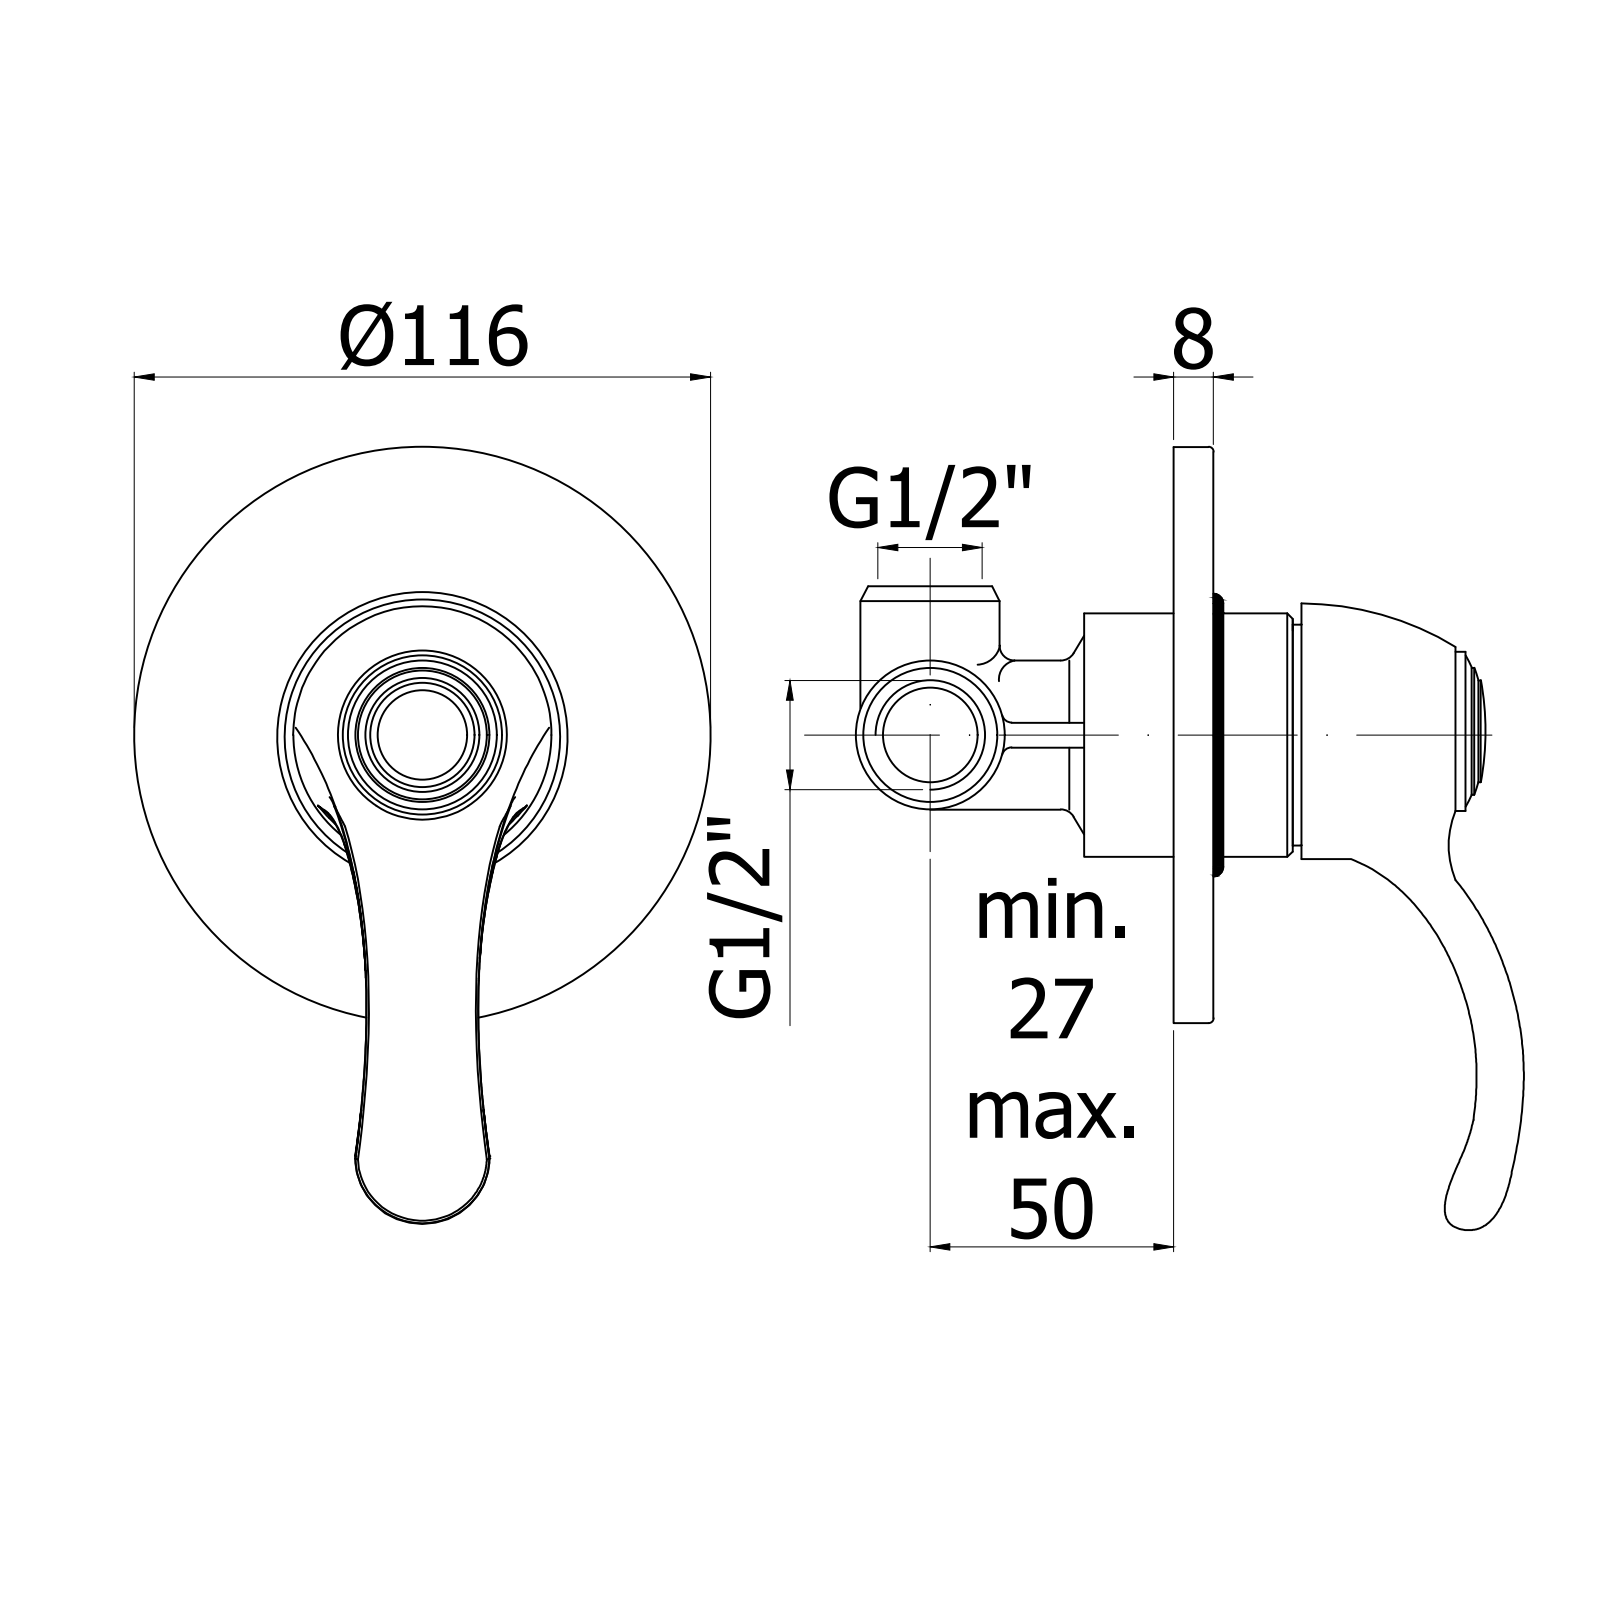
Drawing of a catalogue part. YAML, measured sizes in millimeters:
part_name: "FA010CR"
step_written_by: "CREO PARAMETRIC BY PTC INC, 2020044 (CONFIG_CONTROL_DESIGN)"
units: millimeters
bodies: {solids: 2, faces: 140, planar: 35, cylindrical: 30, other: 75}
overall_size: [156.15, 116, 75.93]
volume: 124292
surface_area: 53427
round_holes:
  - {diameter: 4, count: 1}
  - {diameter: 7, count: 1}
  - {diameter: 30, count: 1}
  - {diameter: 34.5, count: 1}
  - {diameter: 40.5, count: 1}
  - {diameter: 42.5, count: 1}
round_bosses_or_shafts:
  - {diameter: 116, count: 1}
  - {diameter: 56.5, count: 1}
  - {diameter: 50, count: 1}
  - {diameter: 29.9, count: 1}
  - {diameter: 27, count: 1}
partial_cylinders:
  - {radius: 1.5, count: 4}
face_to_face_distances: [0.59, 2.5, 55.4, 54.81, 57.9, 57.31, 9, 11, 10.41, 44.4]
hole_center_spacings: [1.47, 1.62, 11.38, 11.53, 13]
